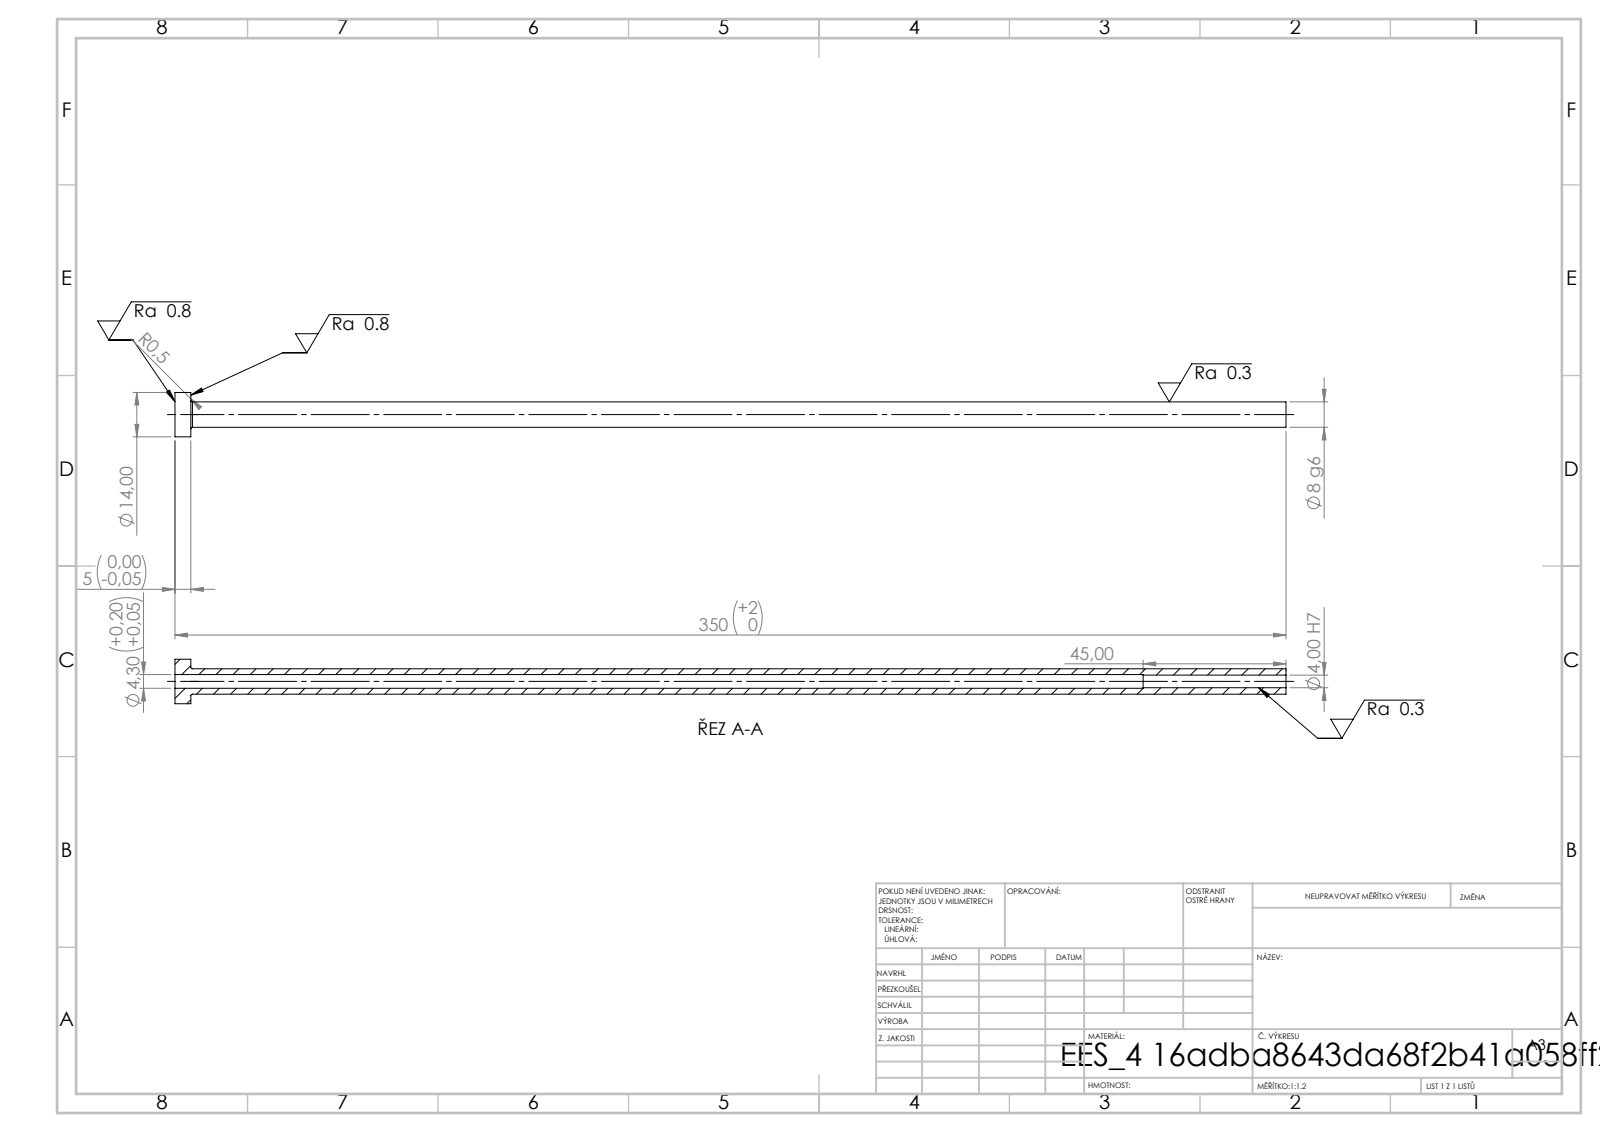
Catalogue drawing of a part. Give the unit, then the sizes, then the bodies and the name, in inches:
Units: inches
Overall size (bounding box): 13.78 × 0.551 × 0.551
Round holes (diameter × count): ⌀0.157 ×1, ⌀0.169 ×1
Round bosses / shafts (diameter × count): ⌀0.551 ×1, ⌀0.315 ×1
Main face-to-face distances: 0.197, 13.78, 13.583, 12.008, 11.811, 1.772
Volume: 0.801 in³ · Surface area: 21.47 in²
Bodies: 1 solid, 14 faces (4 planar, 8 cylindrical, 2 other)
STEP written by: SolidWorks 2019 (CONFIG_CONTROL_DESIGN)
